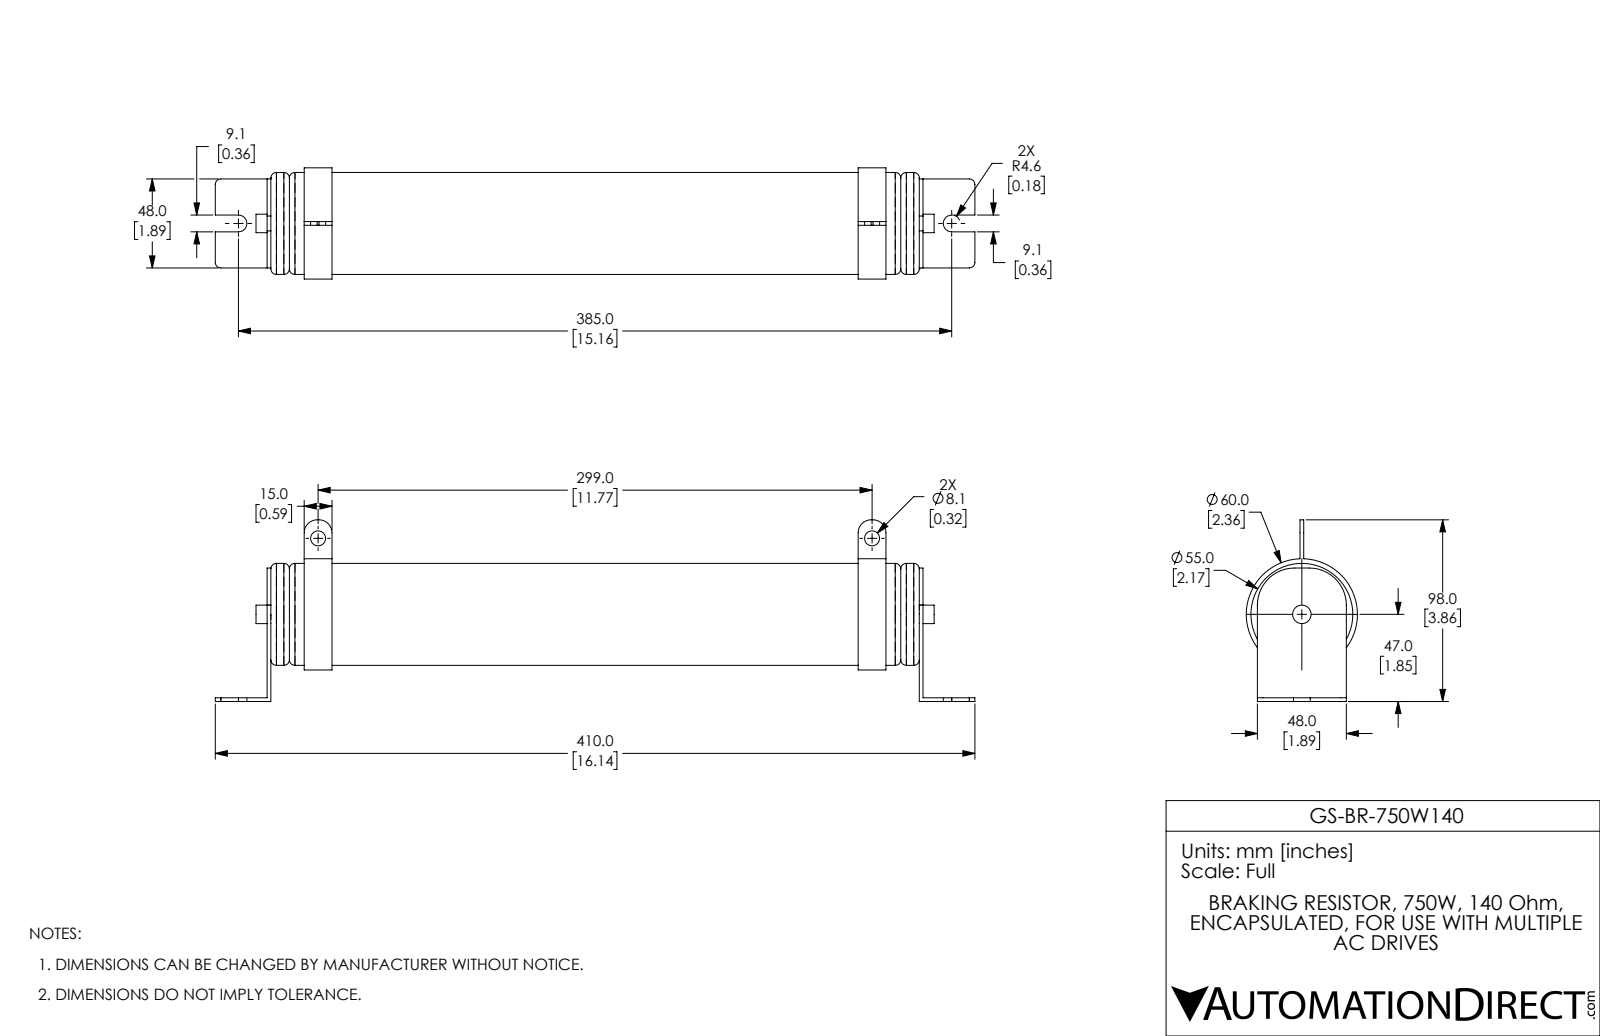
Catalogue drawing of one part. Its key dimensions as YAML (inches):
part_name: "VFD-BR-B2-PD-3D00-BR750W140"
step_written_by: "SolidWorks 2017 (AUTOMOTIVE_DESIGN)"
units: inches
bodies: {solids: 1, faces: 90, planar: 40, cylindrical: 38, other: 12}
overall_size: [16.142, 3.858, 2.362]
volume: 52.66
surface_area: 126
round_holes:
  - {diameter: 0.319, count: 2}
round_bosses_or_shafts:
  - {diameter: 2.362, count: 1}
  - {diameter: 2.165, count: 1}
  - {diameter: 0.394, count: 1}
partial_cylinders:
  - {radius: 0.118, count: 4}
  - {radius: 0.276, count: 4}
  - {radius: 0.179, count: 2}
  - {radius: 0.787, count: 2}
face_to_face_distances: [0.079, 13.937, 13.858, 13.78, 0.787, 13.15, 0.709, 13.071, 1.378, 12.559]
hole_center_spacings: [11.772]
